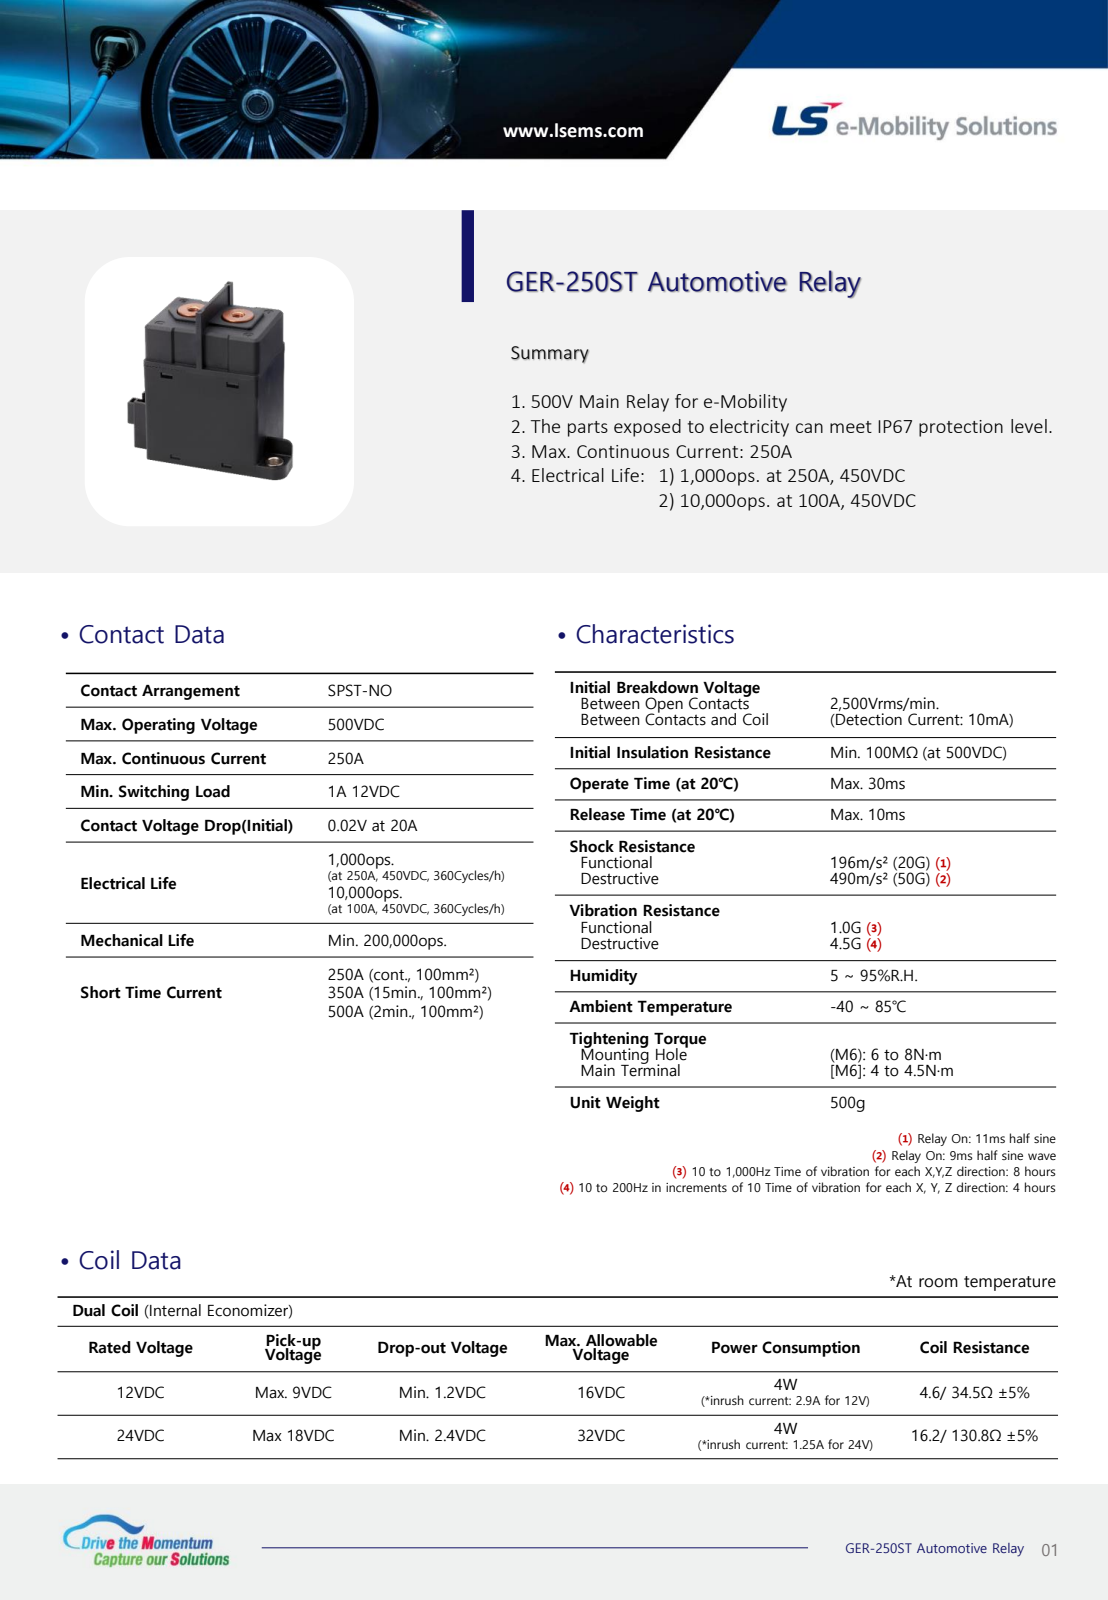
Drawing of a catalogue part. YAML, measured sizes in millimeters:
part_name: "72316604101_TOTAL ASS''Y,SUB,GER250ST_AllCATPart"
step_written_by: "CATIA V5 STEP AP214 (AUTOMOTIVE_DESIGN)"
units: millimeters
bodies: {solids: 9, faces: 1001, planar: 491, cylindrical: 286, other: 224}
overall_size: [91.5, 87, 45]
volume: 43322
surface_area: 56874
round_holes:
  - {diameter: 1, count: 4}
  - {diameter: 5, count: 4}
  - {diameter: 6, count: 2}
  - {diameter: 6.5, count: 2}
  - {diameter: 8.4, count: 2}
  - {diameter: 9.4, count: 2}
  - {diameter: 16.5, count: 2}
round_bosses_or_shafts:
  - {diameter: 16, count: 2}
partial_cylinders:
  - {radius: 0.2, count: 86}
  - {radius: 0.5, count: 47}
  - {radius: 1, count: 18}
  - {radius: 2, count: 15}
  - {radius: 1.1, count: 4}
  - {radius: 3, count: 4}
  - {radius: 0.1, count: 2}
  - {radius: 1.6, count: 2}
face_to_face_distances: [1, 1.8, 9.6, 1.5, 57.4, 41.4, 39.9, 10.6, 8.6, 1.2]
hole_center_spacings: [19.3, 38.74, 9.52, 10.56, 14.01, 30.1, 31, 34.47]
